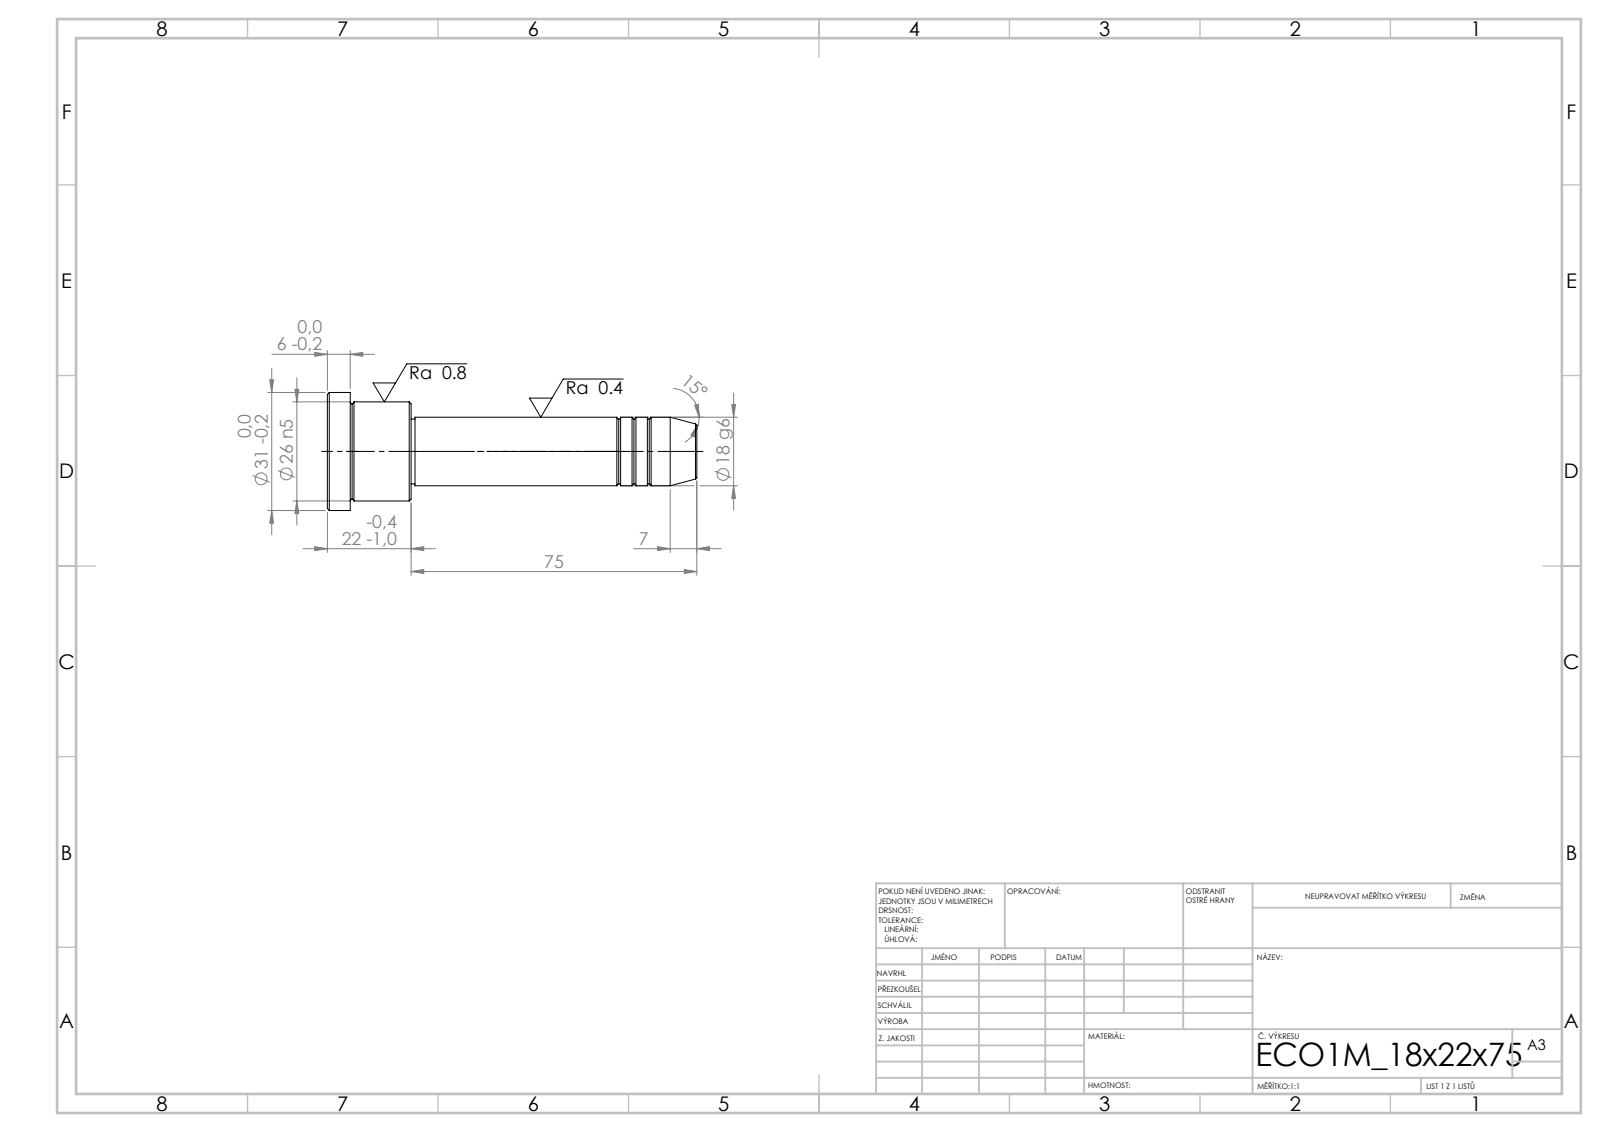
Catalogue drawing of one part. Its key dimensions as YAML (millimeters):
step_written_by: "SolidWorks 2019 (CONFIG_CONTROL_DESIGN)"
units: millimeters
bodies: {solids: 1, faces: 43, planar: 5, cylindrical: 14, other: 24}
overall_size: [97, 31, 31]
volume: 31616
surface_area: 7643
round_bosses_or_shafts:
  - {diameter: 31, count: 1}
  - {diameter: 26, count: 1}
  - {diameter: 18, count: 1}
  - {diameter: 17, count: 1}
face_to_face_distances: [22, 16, 6, 75, 91, 97, 74, 1, 17, 23]
